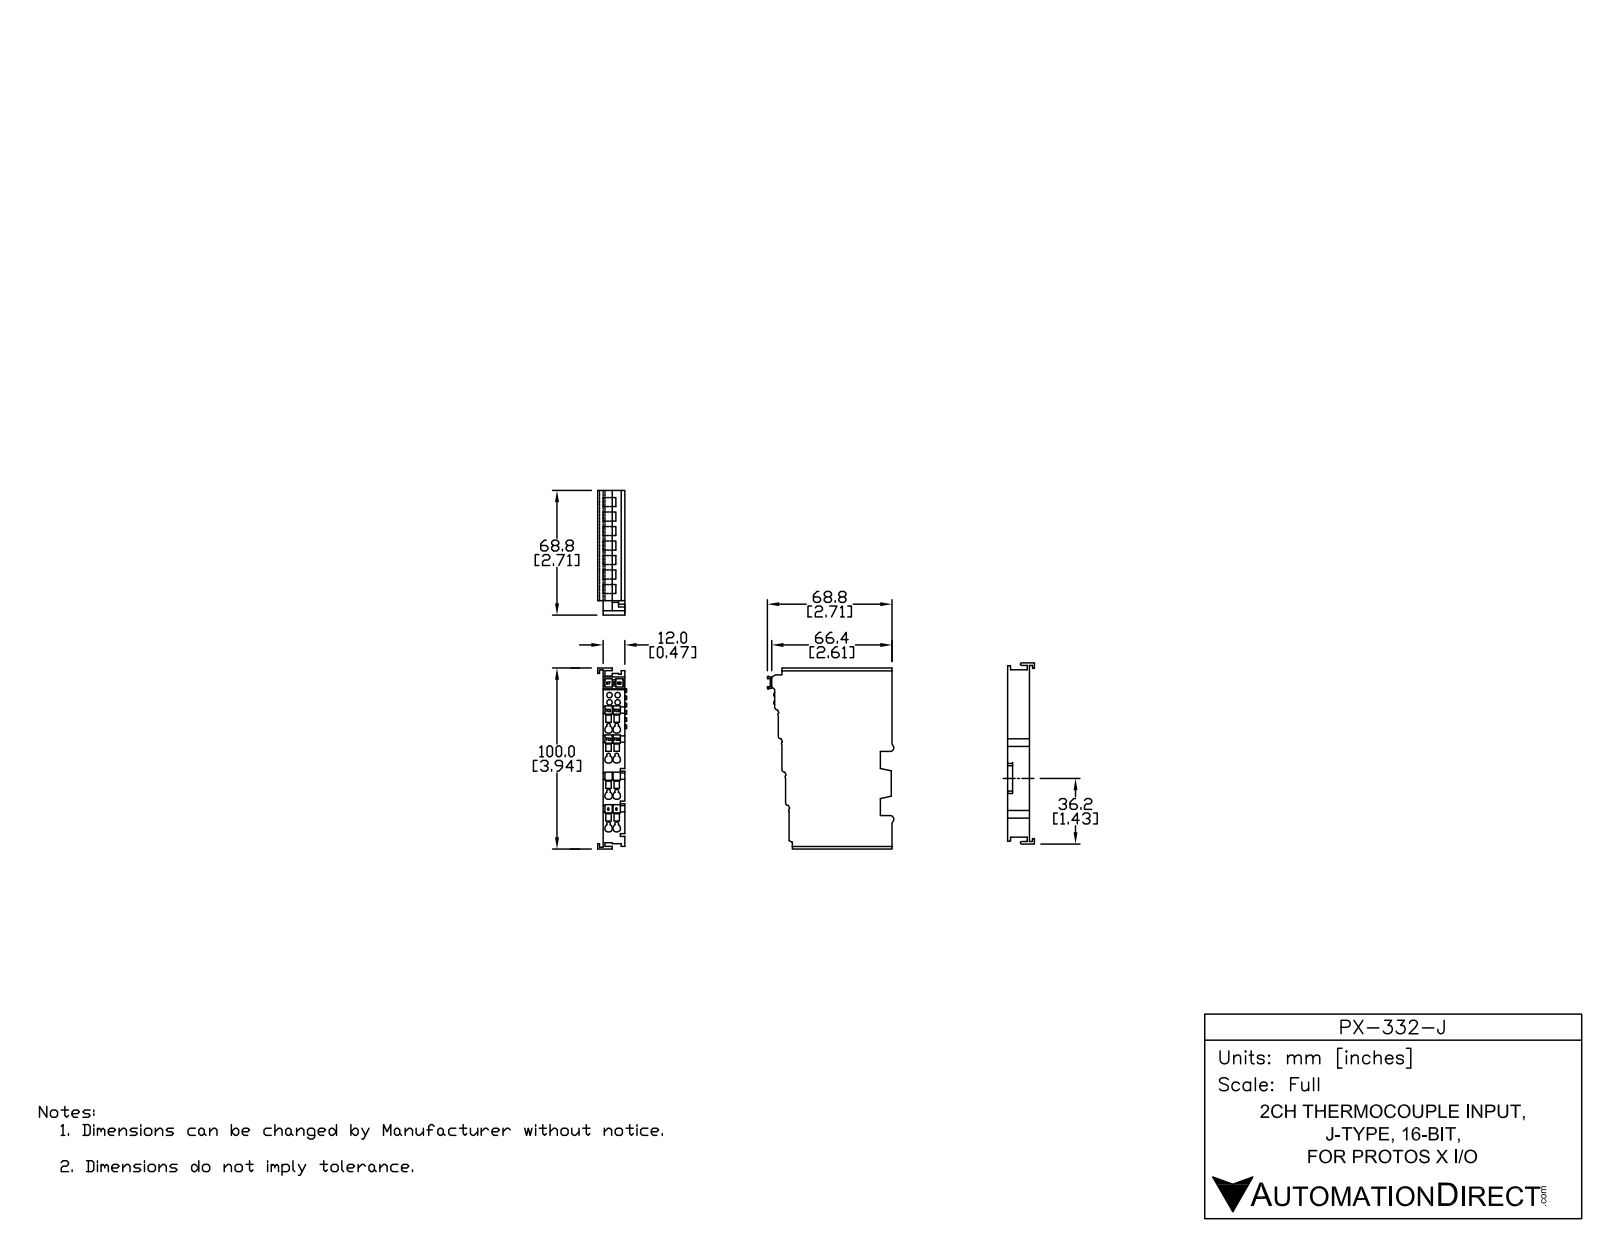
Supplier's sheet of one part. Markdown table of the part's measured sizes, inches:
| quantity | value |
| --- | --- |
| part name | PX-332-J |
| STEP written by | SolidWorks 2014 (AUTOMOTIVE_DESIGN) |
| units | inches |
| bodies | 28 solids, 1367 faces (963 planar, 344 cylindrical, 60 other) |
| overall size | 3.947 × 2.806 × 0.596 |
| volume | 3.564 in³ |
| surface area | 52.52 in² |
| round holes (diameter × count) | 0.157 × 8, 0.138 × 4 |
| partial cylindrical surfaces (radius × count) | 0.012 × 46, 0.01 × 35, 0.015 × 12, 0.005 × 10, 0.039 × 9, 0.016 × 8, 0.007 × 4, 0.041 × 4 |
| main face-to-face distances | 0.472, 0.039, 0.079, 0.394, 0.073, 0.433, 0.343, 0.157, 0.124, 0.048 |
| hole center spacings | 0.177, 0.197, 0.724, 0.751, 0.25, 0.63, 0.66, 0.804 |
